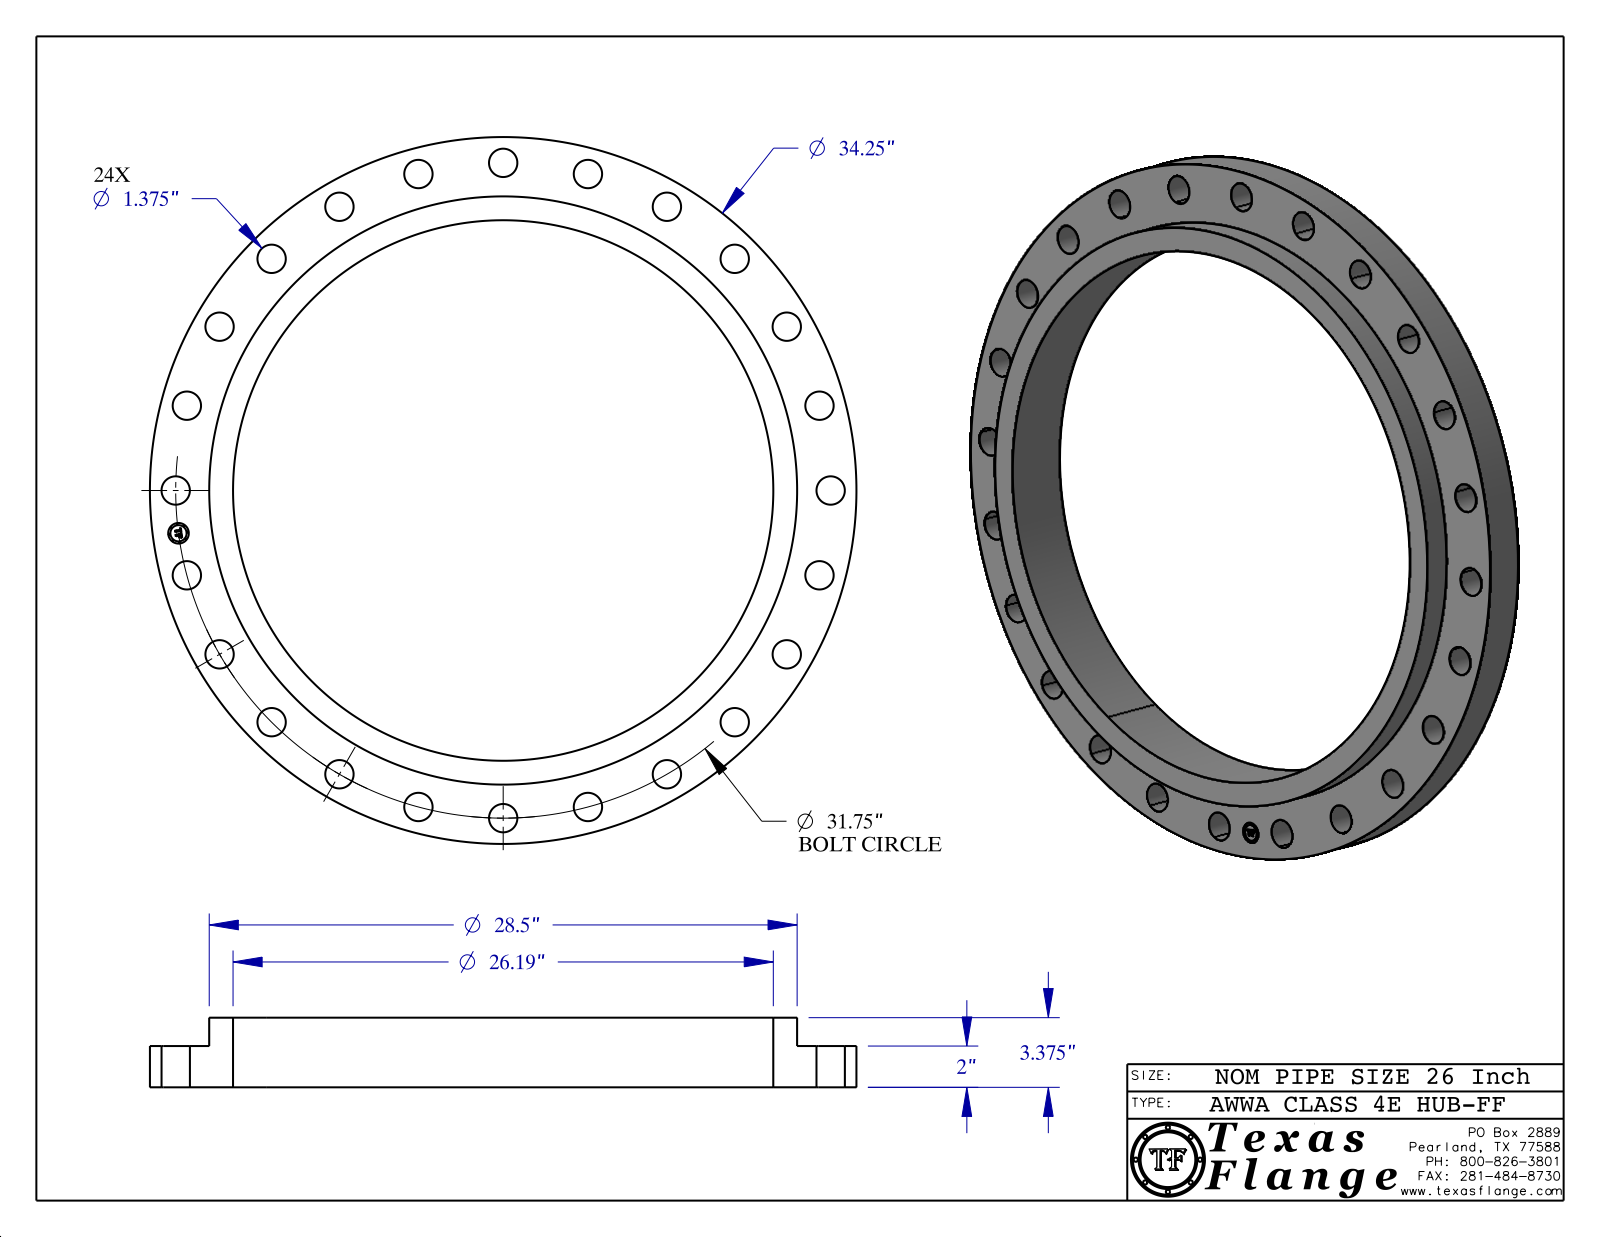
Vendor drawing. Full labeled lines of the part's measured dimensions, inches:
Part name (STEP PRODUCT): AWWA Class 4E-HUB-FF
STEP written by: CATIA V5 STEP AP214 (AUTOMOTIVE_DESIGN)
Units: inches
Bodies: 1 solid, 442 faces (368 planar, 74 cylindrical, 0 other)
Overall size (bounding box): 34.25 × 34.25 × 3.375
Volume: 830.4 in³ · Surface area: 1 517 in²
Round holes (diameter × count): ⌀1.375 ×24, ⌀1 ×1, ⌀26.19 ×1
Round bosses / shafts (diameter × count): ⌀0.061 ×8, ⌀34.25 ×1, ⌀28.5 ×1, ⌀0.788 ×1
Main face-to-face distances: 2, 3.375, 1.375, 1.985, 0.015, 1.39, 0.298, 0.292, 0.054, 0.193
Hole centre spacings: 15.875, 15.875, 29.333, 27.496, 4.144, 8.217, 12.15, 19.328
